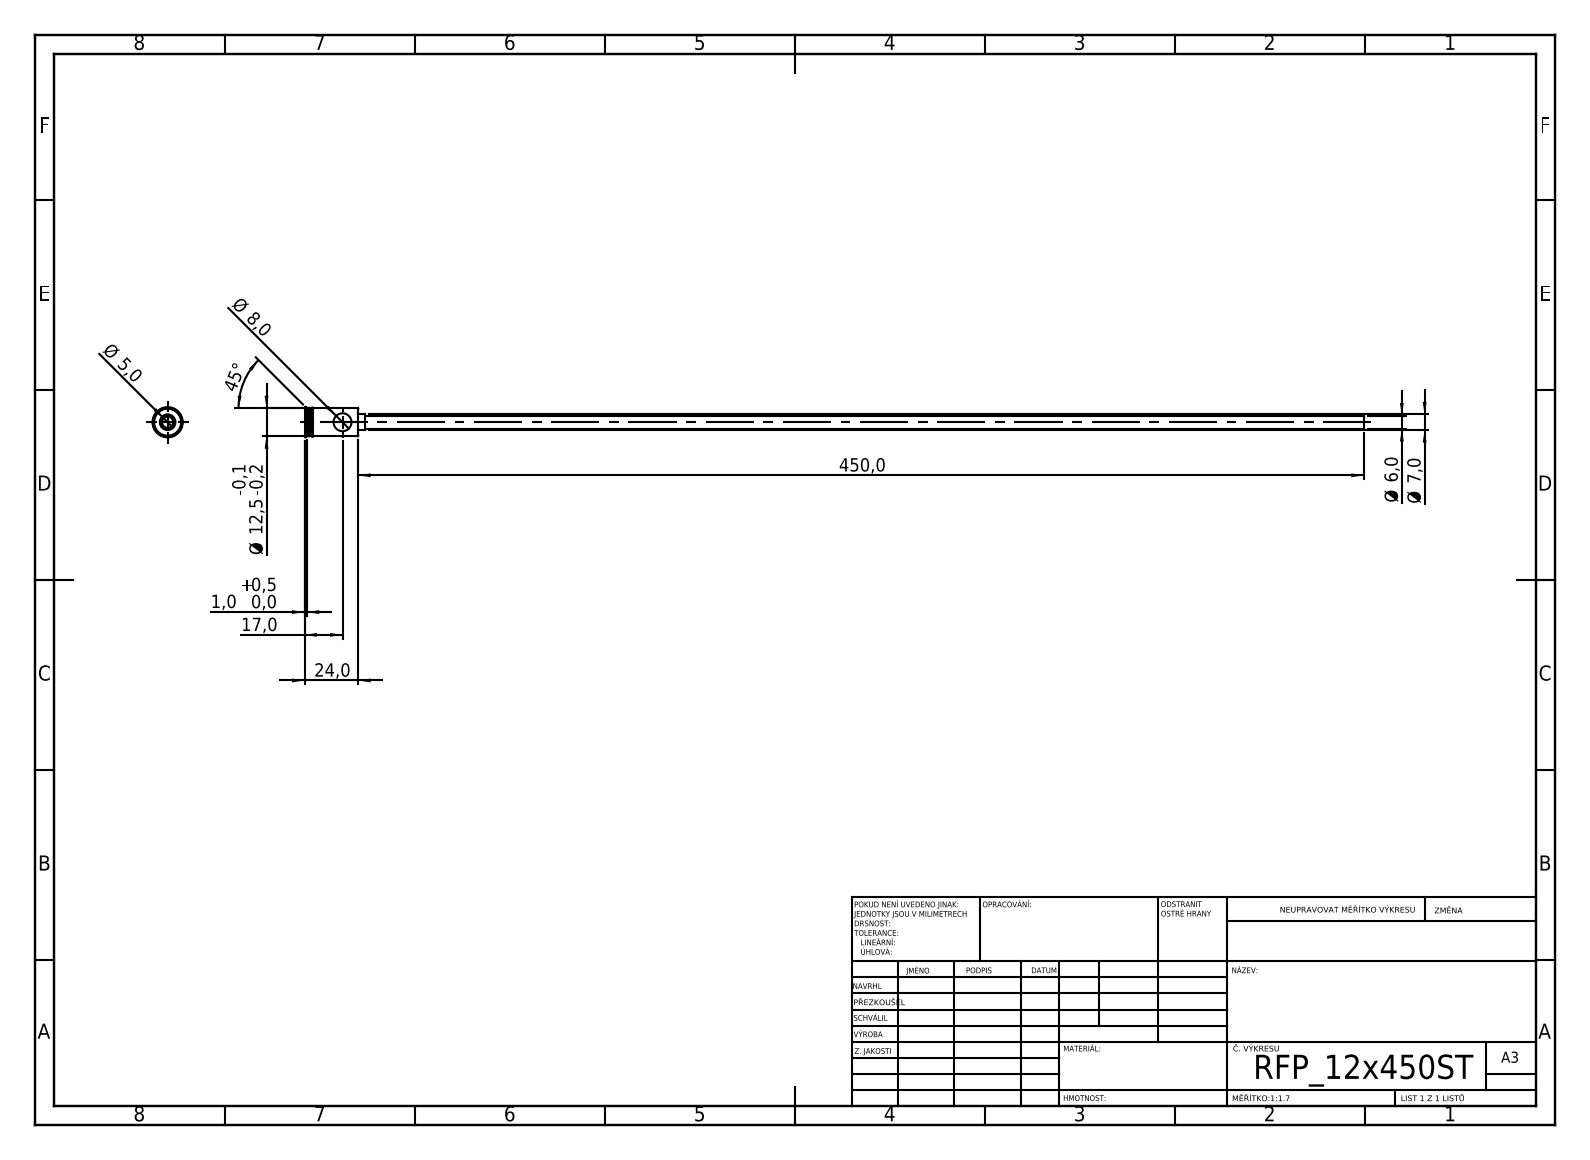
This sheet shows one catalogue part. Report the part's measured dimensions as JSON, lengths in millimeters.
{"step_written_by": "SolidWorks 2019 (CONFIG_CONTROL_DESIGN)", "units": "millimeters", "bodies": {"solids": 1, "faces": 44, "planar": 20, "cylindrical": 16, "other": 8}, "overall_size": [474, 13.5, 13.5], "volume_mm3": 6115, "surface_area_mm2": 17044, "round_holes": [[5, 1], [8, 1]], "round_bosses_or_shafts": [[13.5, 1], [12.5, 1], [7, 1], [6, 1]], "face_to_face_distances": [24, 22, 2, 7.9, 21.7, 2.3, 3, 24.7, 25, 27]}
